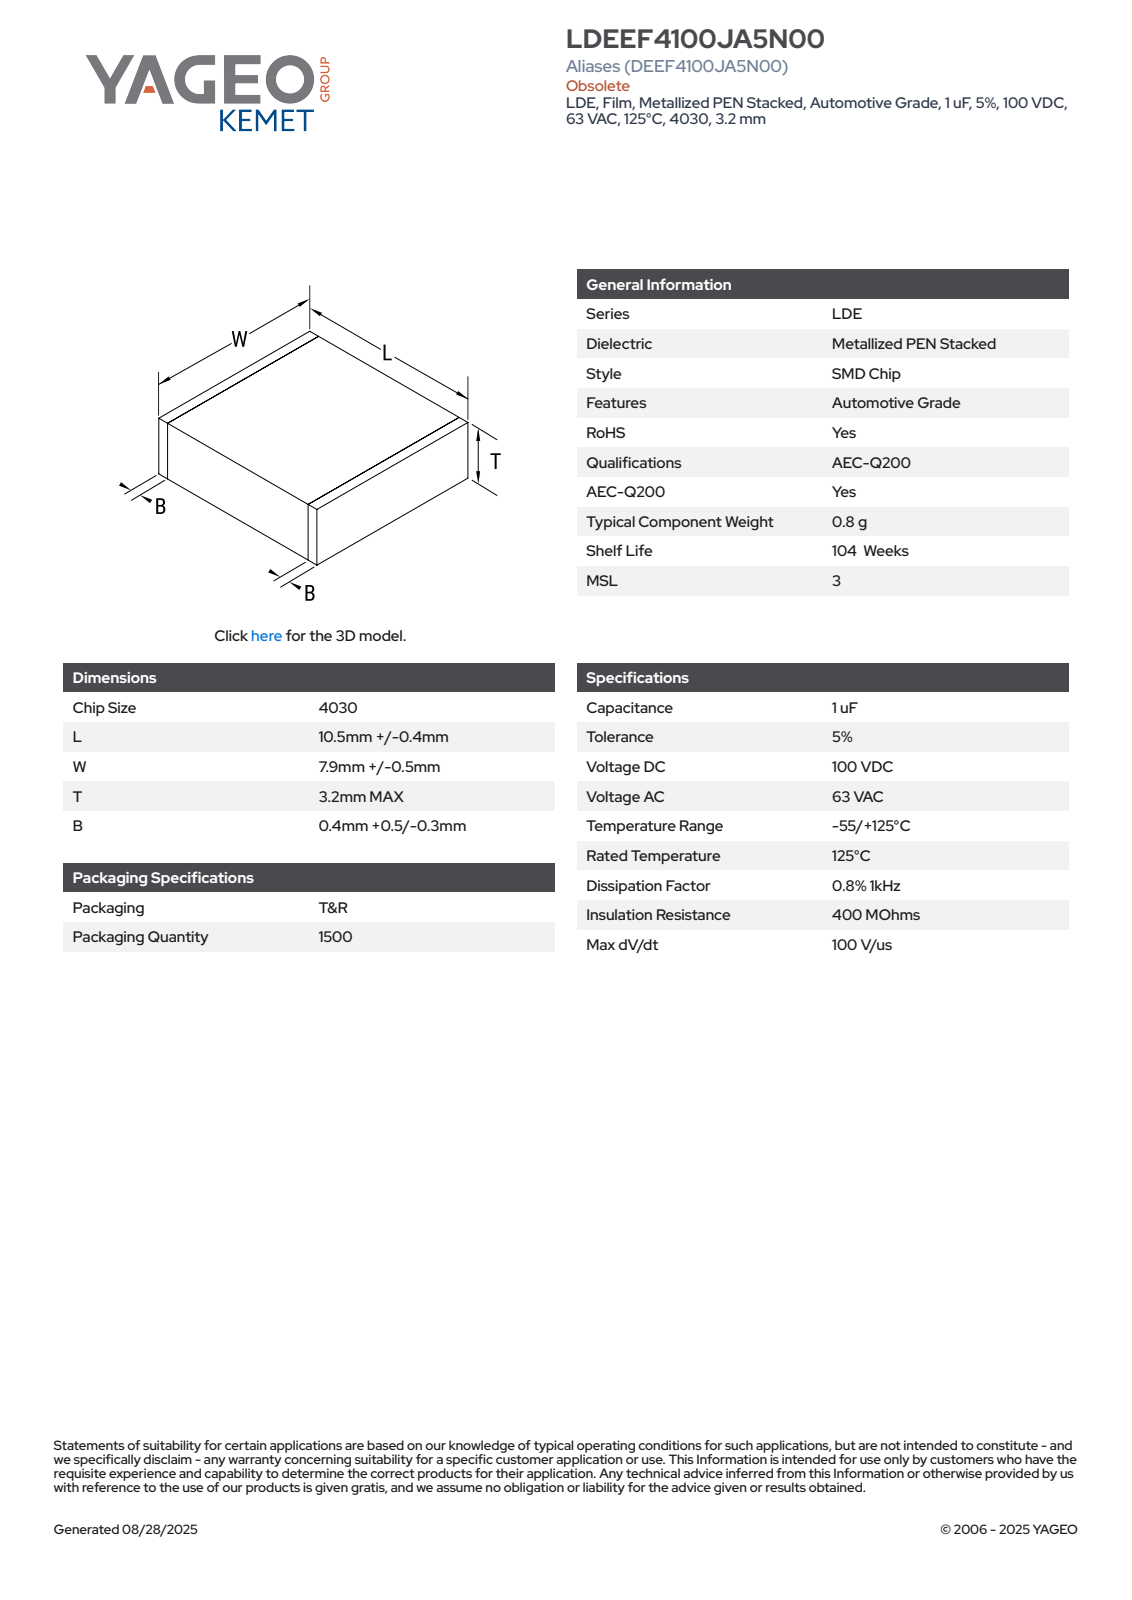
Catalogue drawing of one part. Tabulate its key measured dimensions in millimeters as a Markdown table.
| quantity | value |
| --- | --- |
| part name | CFS_LDELDB_4030_L10.9W8.4T3.2B0.9 |
| STEP written by | SolidWorks 2020 (AUTOMOTIVE_DESIGN) |
| units | millimeters |
| bodies | 4 solids, 73 faces (73 planar, 0 cylindrical, 0 other) |
| overall size | 10.9 × 8.4 × 3.2 |
| volume | 291 mm³ |
| surface area | 312 mm² |
| main face-to-face distances | 3.18, 8.38, 10.9, 3.19, 3.2, 8.39, 8.4, 0.5, 10.4, 9.9 |
